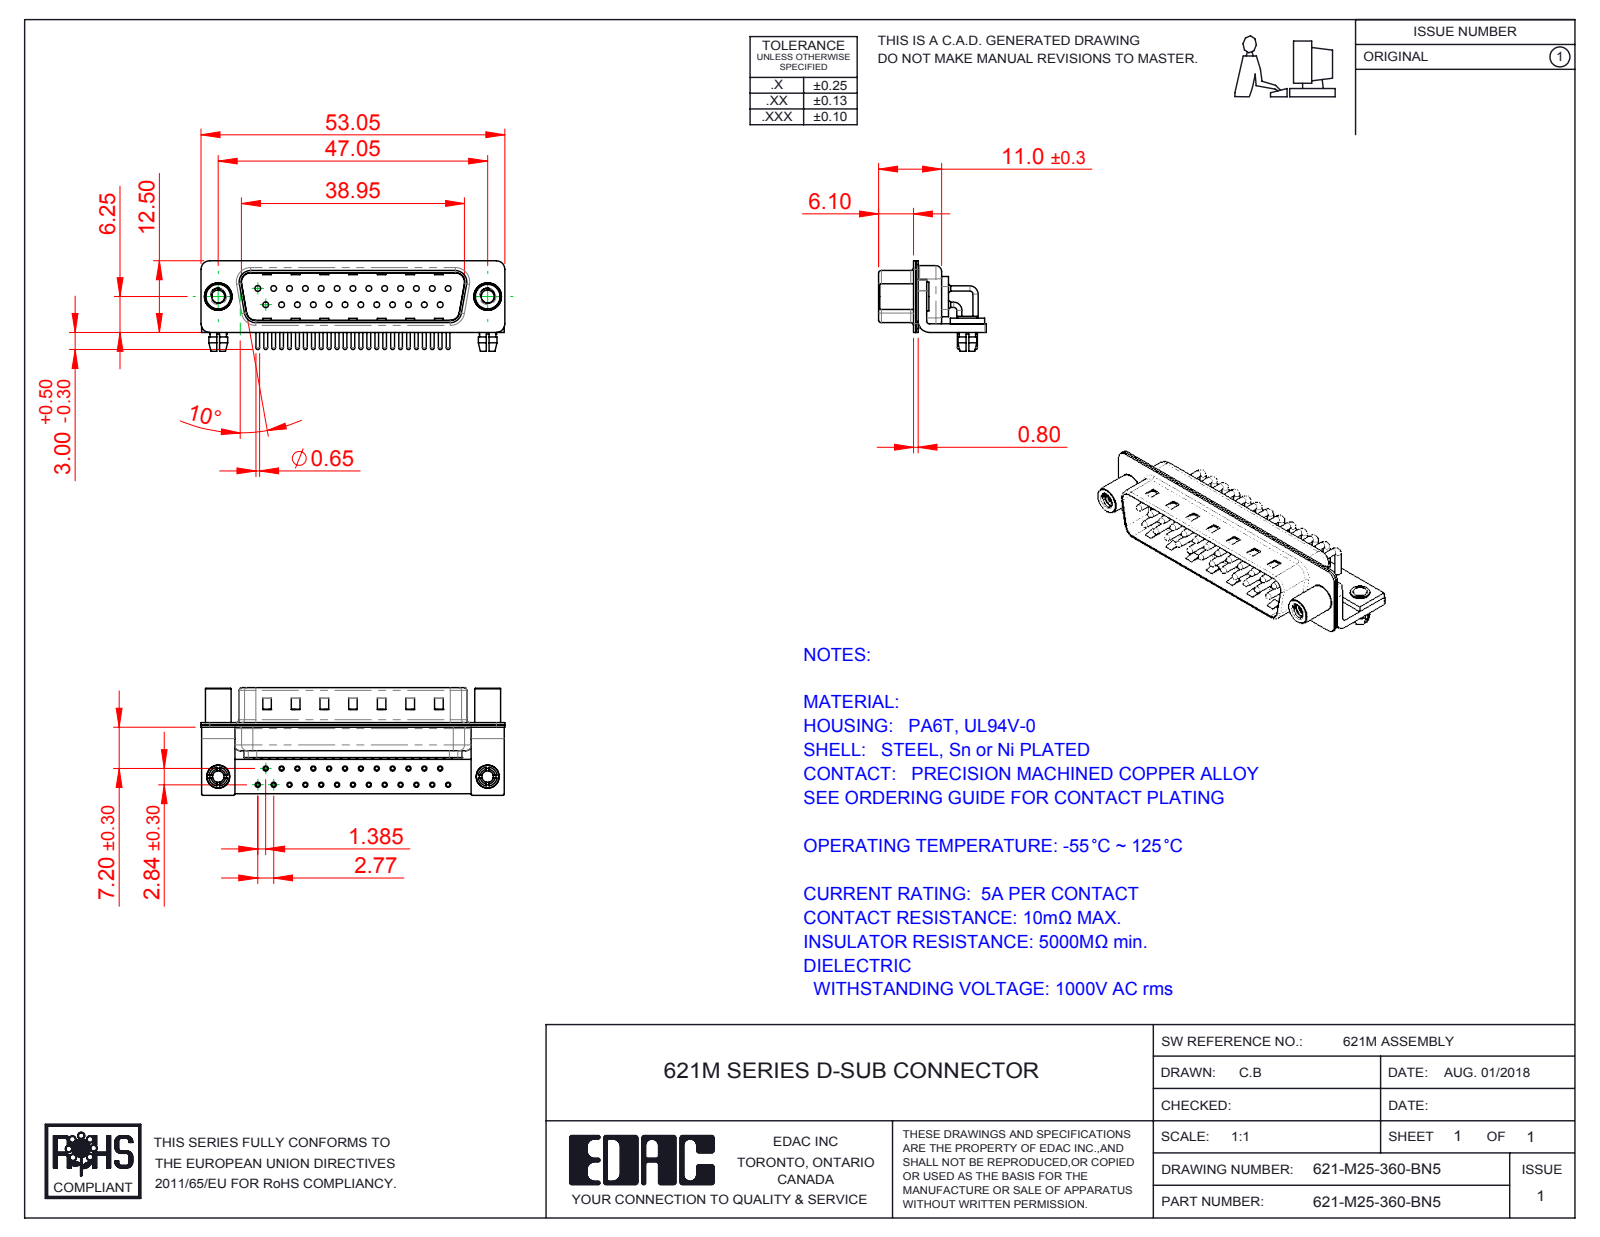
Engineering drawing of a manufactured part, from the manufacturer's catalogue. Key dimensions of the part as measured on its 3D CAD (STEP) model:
Part name (STEP PRODUCT): 621M Contact Row 2; 621M Shell Front_25 Contacts; 621M Shell Rear_25 Contacts; 621-M25-360-BN5 (+6 more)
STEP written by: SolidWorks 2016 (CONFIG_CONTROL_DESIGN)
Units: millimetres
Bodies: 35 solids, 3368 faces (1847 planar, 1183 cylindrical, 338 other)
Overall size (bounding box): 53.05 × 18.8 × 15.8
Volume: 3 558 mm³ · Surface area: 9 450 mm²
Round holes (diameter × count): ⌀2 ×27, ⌀0.9 ×25, ⌀1 ×25, ⌀1.7 ×25, ⌀2.26 ×2, ⌀2.5 ×2, ⌀3.2 ×2, ⌀4 ×2, ⌀4.8 ×2
Round bosses / shafts (diameter × count): ⌀0.9 ×33, ⌀1.5 ×25, ⌀0.65 ×25, ⌀5 ×2, ⌀4.9 ×2, ⌀4.5 ×2, ⌀4 ×2, ⌀3.4 ×2
Partial cylindrical surfaces — rounded edges, fillets, slot ends (radius × count): R1.01 ×25, R0.25 ×16, R1.5 ×16, R2 ×13, R0.5 ×9, R1.6 ×8, R0.6 ×4, R0.65 ×4
Main face-to-face distances: 0.4, 0.85, 1.25, 1.5, 9.55, 0.8, 10.4, 8.3, 1, 1.9
Hole centre spacings: 3.16, 2.77, 8.31, 5.54, 11.08, 13.85, 5.04, 16.62
